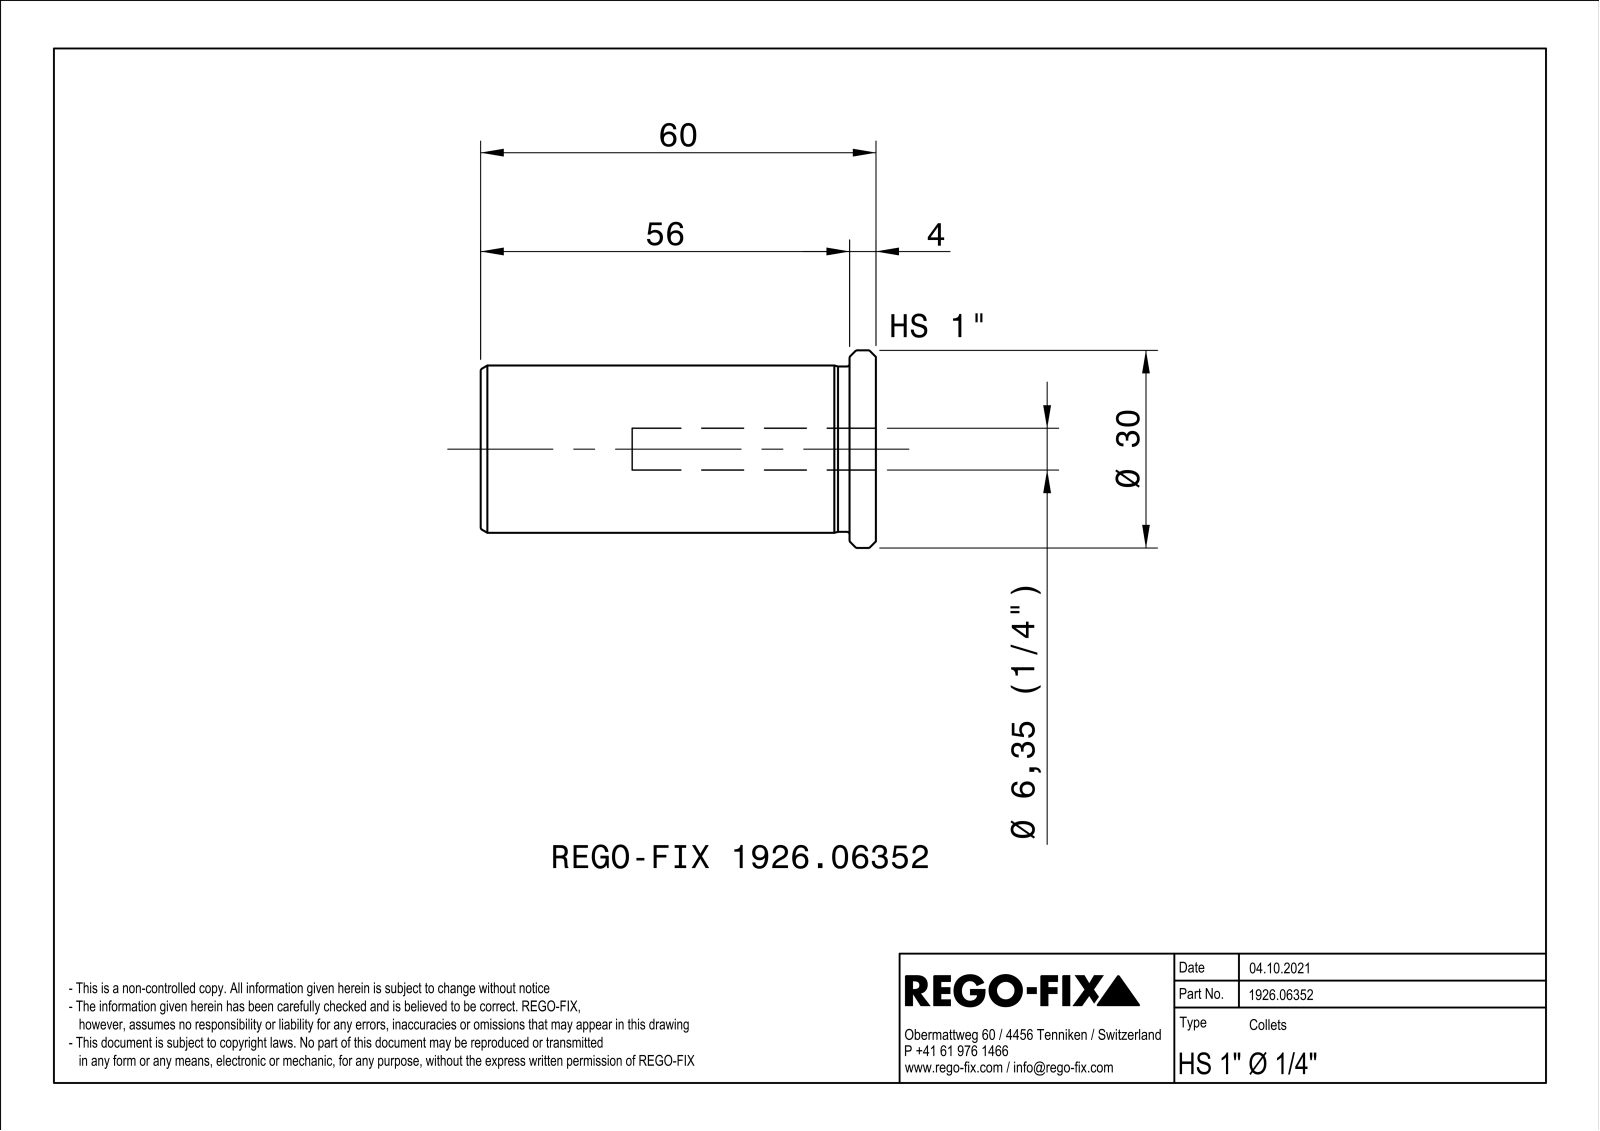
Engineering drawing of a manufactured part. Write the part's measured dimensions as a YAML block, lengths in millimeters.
part_name: "NOCUT"
step_written_by: "SIEMENS PLM Software Solid Edge ST10 (AUTOMOTIVE_DESIGN)"
units: millimeters
bodies: {solids: 1, faces: 72, planar: 22, cylindrical: 12, other: 38}
overall_size: [60, 29.98, 29.98]
volume: 23744
surface_area: 10124
round_holes:
  - {diameter: 6.35, count: 1}
  - {diameter: 10, count: 1}
  - {diameter: 20.5, count: 1}
round_bosses_or_shafts:
  - {diameter: 30, count: 1}
  - {diameter: 25.4, count: 1}
  - {diameter: 25.1, count: 1}
face_to_face_distances: [1, 60, 4, 56]
